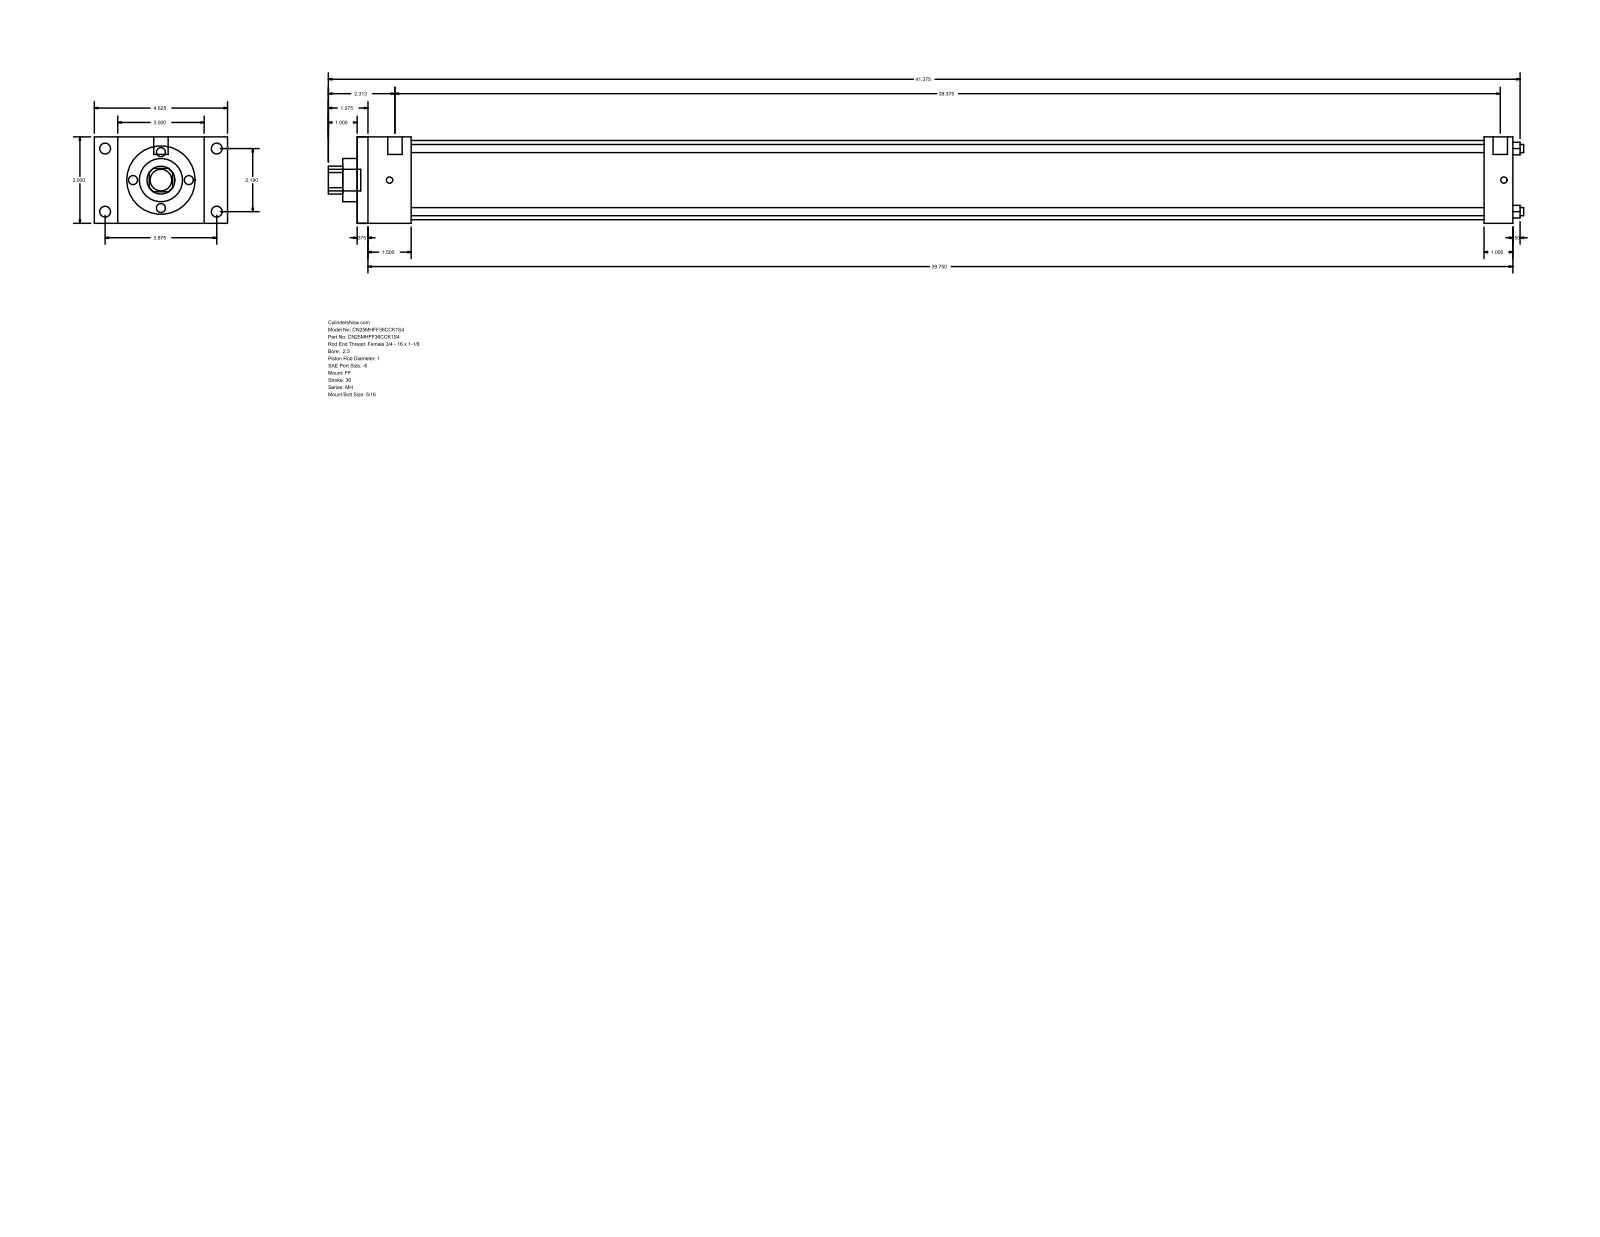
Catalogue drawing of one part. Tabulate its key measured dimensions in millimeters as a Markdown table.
| quantity | value |
| --- | --- |
| part name | MH_FF__0250_1 |
| STEP written by | GSSL Pune (CONFIG_CONTROL_DESIGN) |
| units | millimeters |
| bodies | 0 solids, 92 faces (64 planar, 28 cylindrical, 0 other) |
| overall size | 1054.1 × 117.47 × 76.2 |
| round holes (diameter × count) | 7.14 × 4, 25.4 × 1, 38.1 × 1, 69.85 × 1 |
| round bosses / shafts (diameter × count) | 9.53 × 4, 5.56 × 4, 12.7 × 2, 19.05 × 1 |
| partial cylindrical surfaces (radius × count) | 12.29 × 1 |
| main face-to-face distances | 76.2, 1019.18, 9.52, 1009.66, 47.63, 993.77, 38.11, 984.25, 946.14, 971.55 |
| hole center spacings | 39.33, 55.62, 78.66 |
